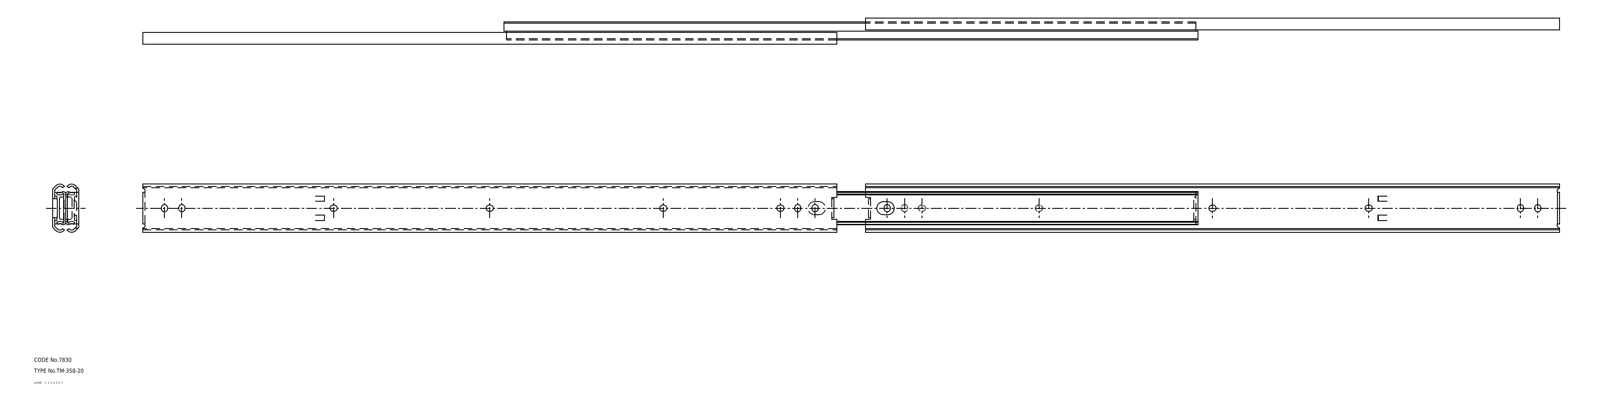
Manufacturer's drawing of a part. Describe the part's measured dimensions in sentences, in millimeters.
The part is named "member_B; member_A1^TM_358_20; TM_358_20". Its 3-D file was written by "SolidWorks 2015 (AUTOMOTIVE_DESIGN)". It is 3 solids with 222 faces: 126 planar, 96 cylindrical and 0 other. Overall it measures 1037 by 35.3 by 19.2 millimeters. Its volume is 126 180 cubic millimeters and its surface area 145 043 square millimeters. Partial cylindrical surfaces (rounded edges, fillets, slot ends): 32 of radius 2.25, 10 of radius 1.6, 8 of radius 1, 8 of radius 2.4, 8 of radius 4, 4 of radius 0.2, 4 of radius 1.3, 4 of radius 1.8. The main face-to-face distances are 1.6, 17.6, 8, 9.6, 11.2, 6.4, 16, 19.2, 3.2, 31.8.
